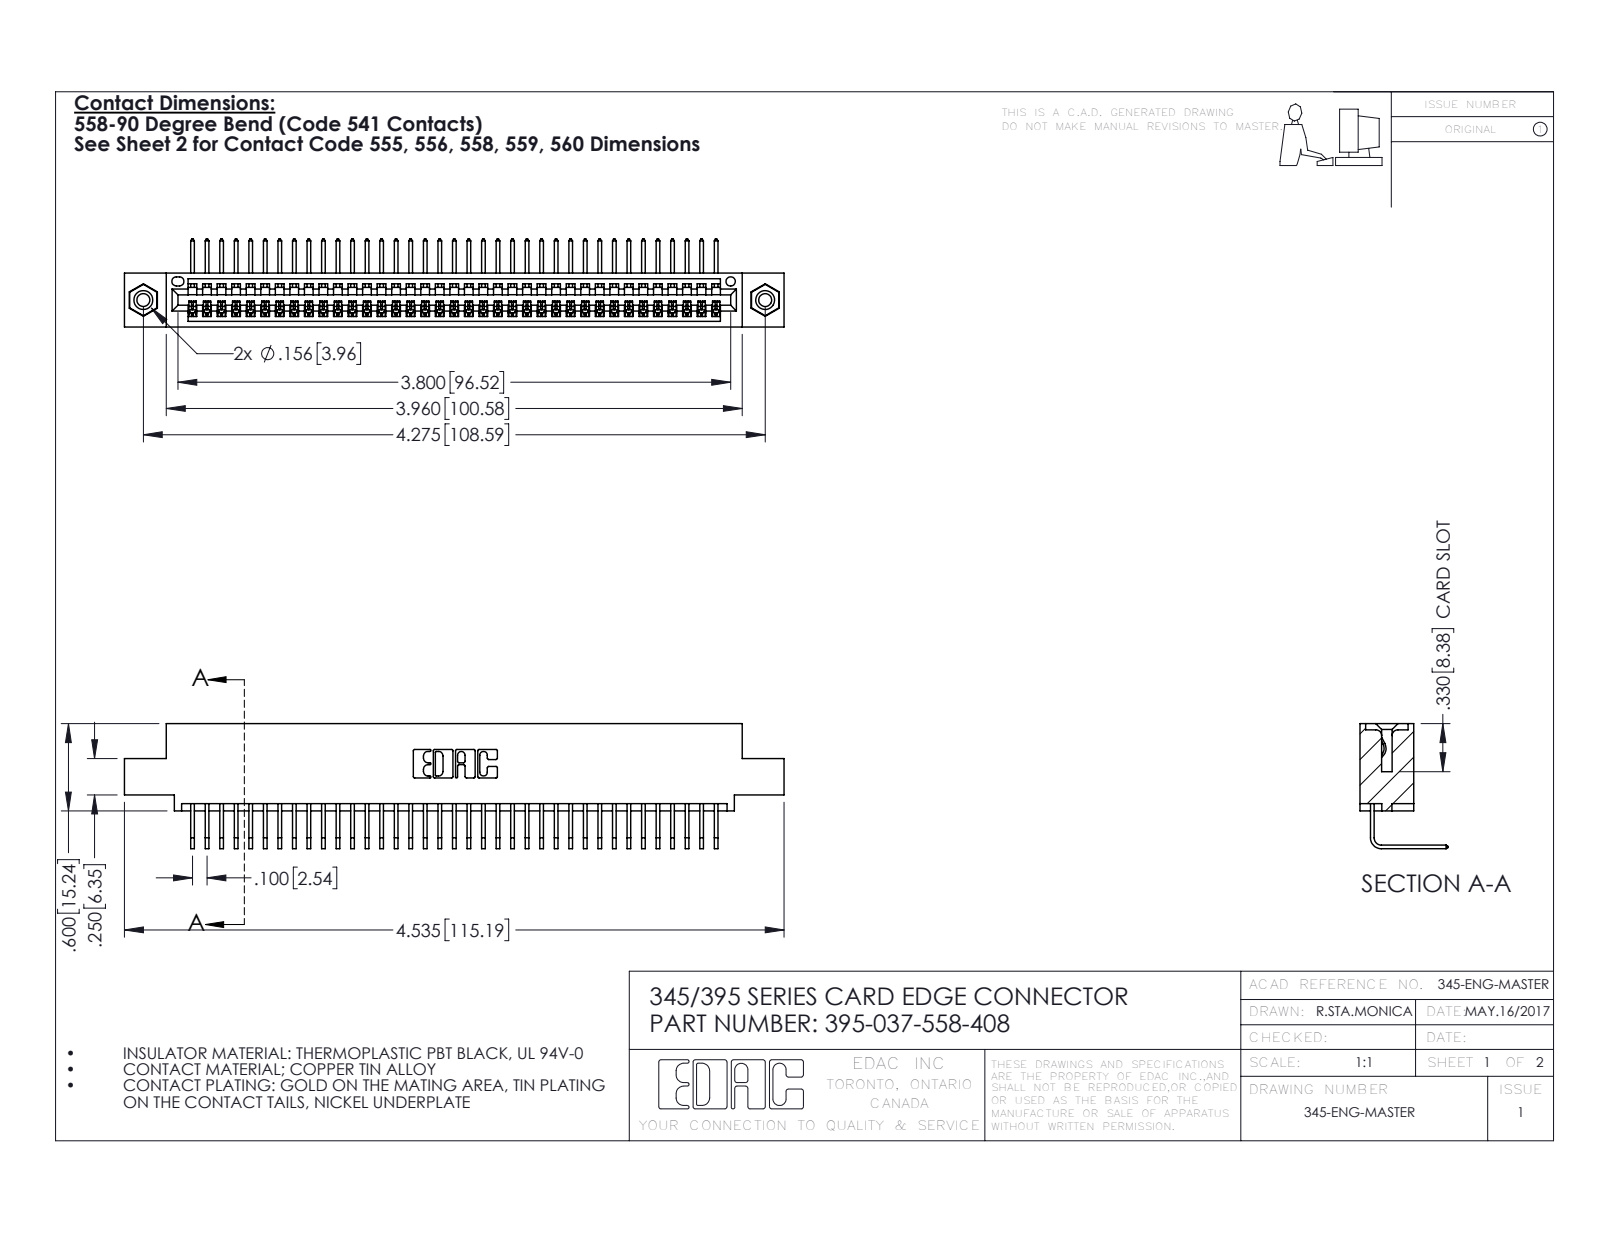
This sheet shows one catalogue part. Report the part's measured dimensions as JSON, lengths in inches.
{"part_name": "345-292-001_558 Tail - 2; 345-250-001_345-250-003-102; 345 Part_0.110 Offset - 0.156 Dia-TI; 395-037-558-408", "step_written_by": "SolidWorks 2016 (CONFIG_CONTROL_DESIGN)", "units": "inches", "bodies": {"solids": 40, "faces": 2410, "planar": 1670, "cylindrical": 724, "other": 16}, "overall_size": [4.535, 0.859, 0.605], "volume_in3": 0.668, "surface_area_in2": 23.72, "round_holes": [[0.089, 2], [0.125, 2], [0.156, 2], [0.064, 1]], "round_bosses_or_shafts": [[0.155, 2]], "partial_cylinders_radius": [[0.006, 74], [0.01, 22], [0.007, 6], [0.031, 6], [0.026, 3], [0.031, 2], [0.04, 2], [0.014, 1]], "face_to_face_distances": [0.072, 0.298, 0.37, 0.2, 0.098, 0.272, 0.025, 0.225, 0.149, 0.072], "hole_center_spacings": [0.27, 4.039, 4.275]}
